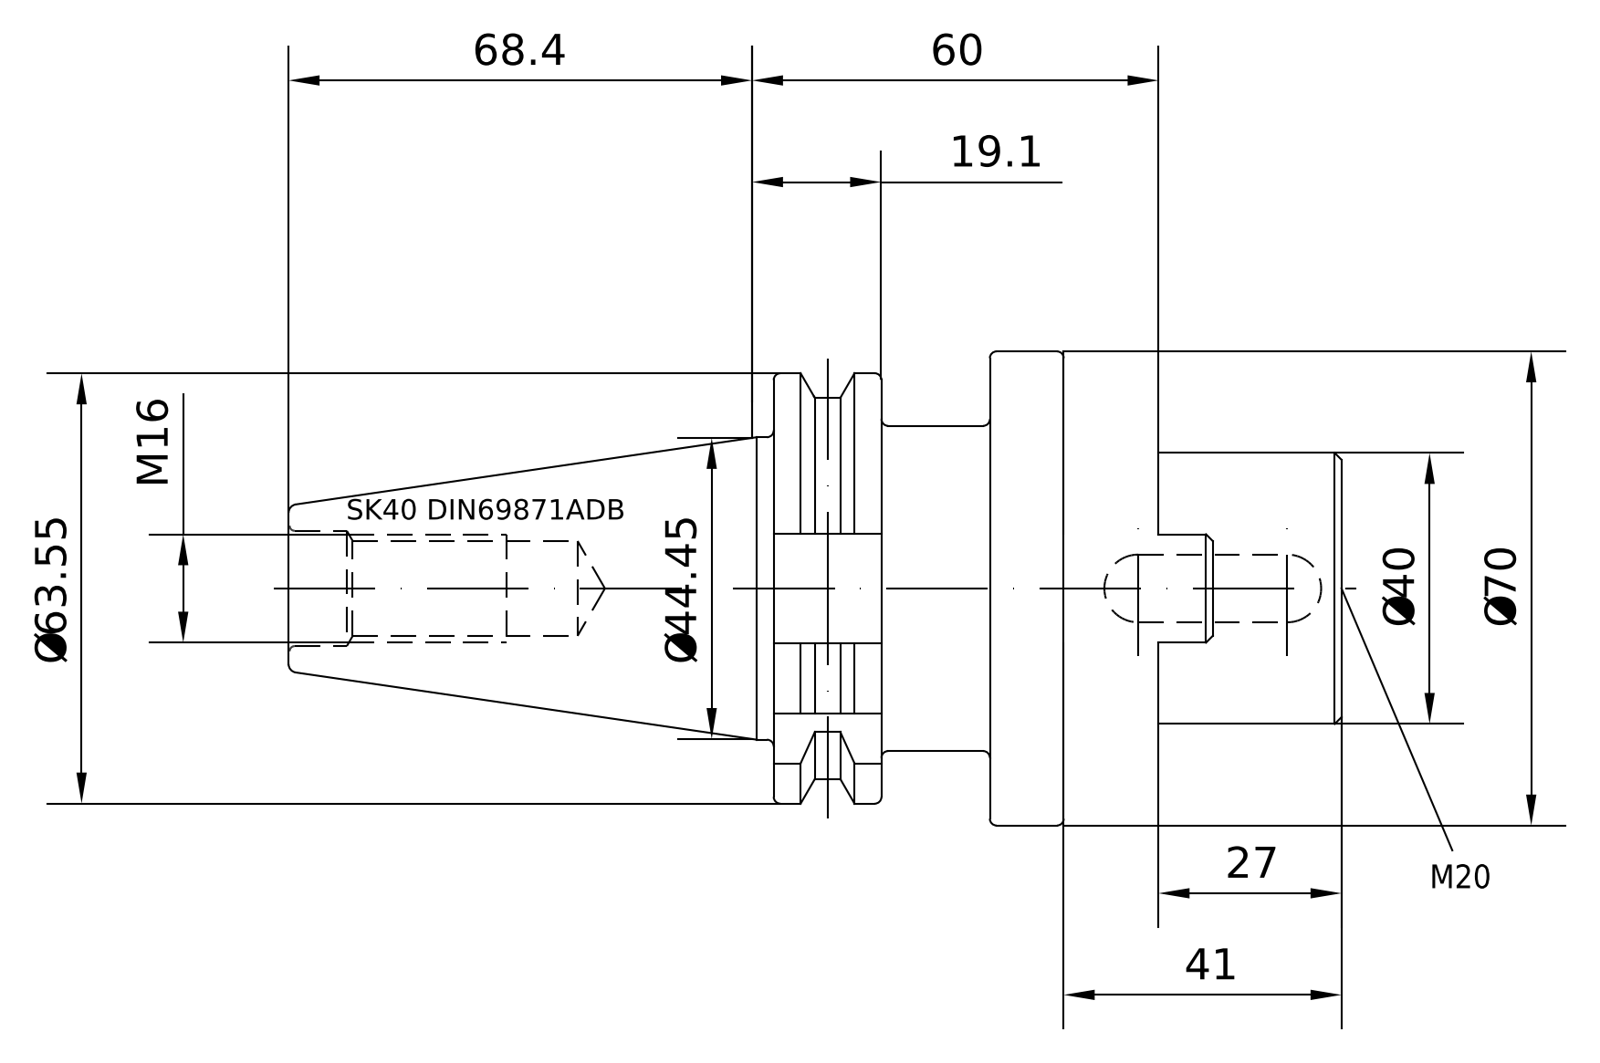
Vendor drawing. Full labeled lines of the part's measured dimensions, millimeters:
Part name (STEP PRODUCT): 40-340-40; 85-200-40; 40-340-40_ASM
STEP written by: PRO/ENGINEER BY PARAMETRIC TECHNOLOGY CORPORATION, 2010430 (CONFIG_CONTROL_DESIGN)
Units: millimetres
Bodies: 2 solids, 197 faces (90 planar, 45 cylindrical, 62 other)
Overall size (bounding box): 155.25 × 70 × 70
Volume: 251 236 mm³ · Surface area: 50 431 mm²
Round holes (diameter × count): ⌀13.84 ×1, ⌀17.01 ×1, ⌀17.5 ×1, ⌀20 ×1, ⌀40.39 ×1, ⌀45 ×1
Round bosses / shafts (diameter × count): ⌀70 ×1, ⌀48 ×1, ⌀43.75 ×1, ⌀40 ×1, ⌀16.01 ×1
Partial cylindrical surfaces — rounded edges, fillets, slot ends (radius × count): R1.35 ×5, R4 ×2, R8.05 ×1, R28 ×1, R31.76 ×1
Main face-to-face distances: 14, 24.95, 10.95, 31.85, 42.8, 56.8, 83.8, 51.95, 41, 27
